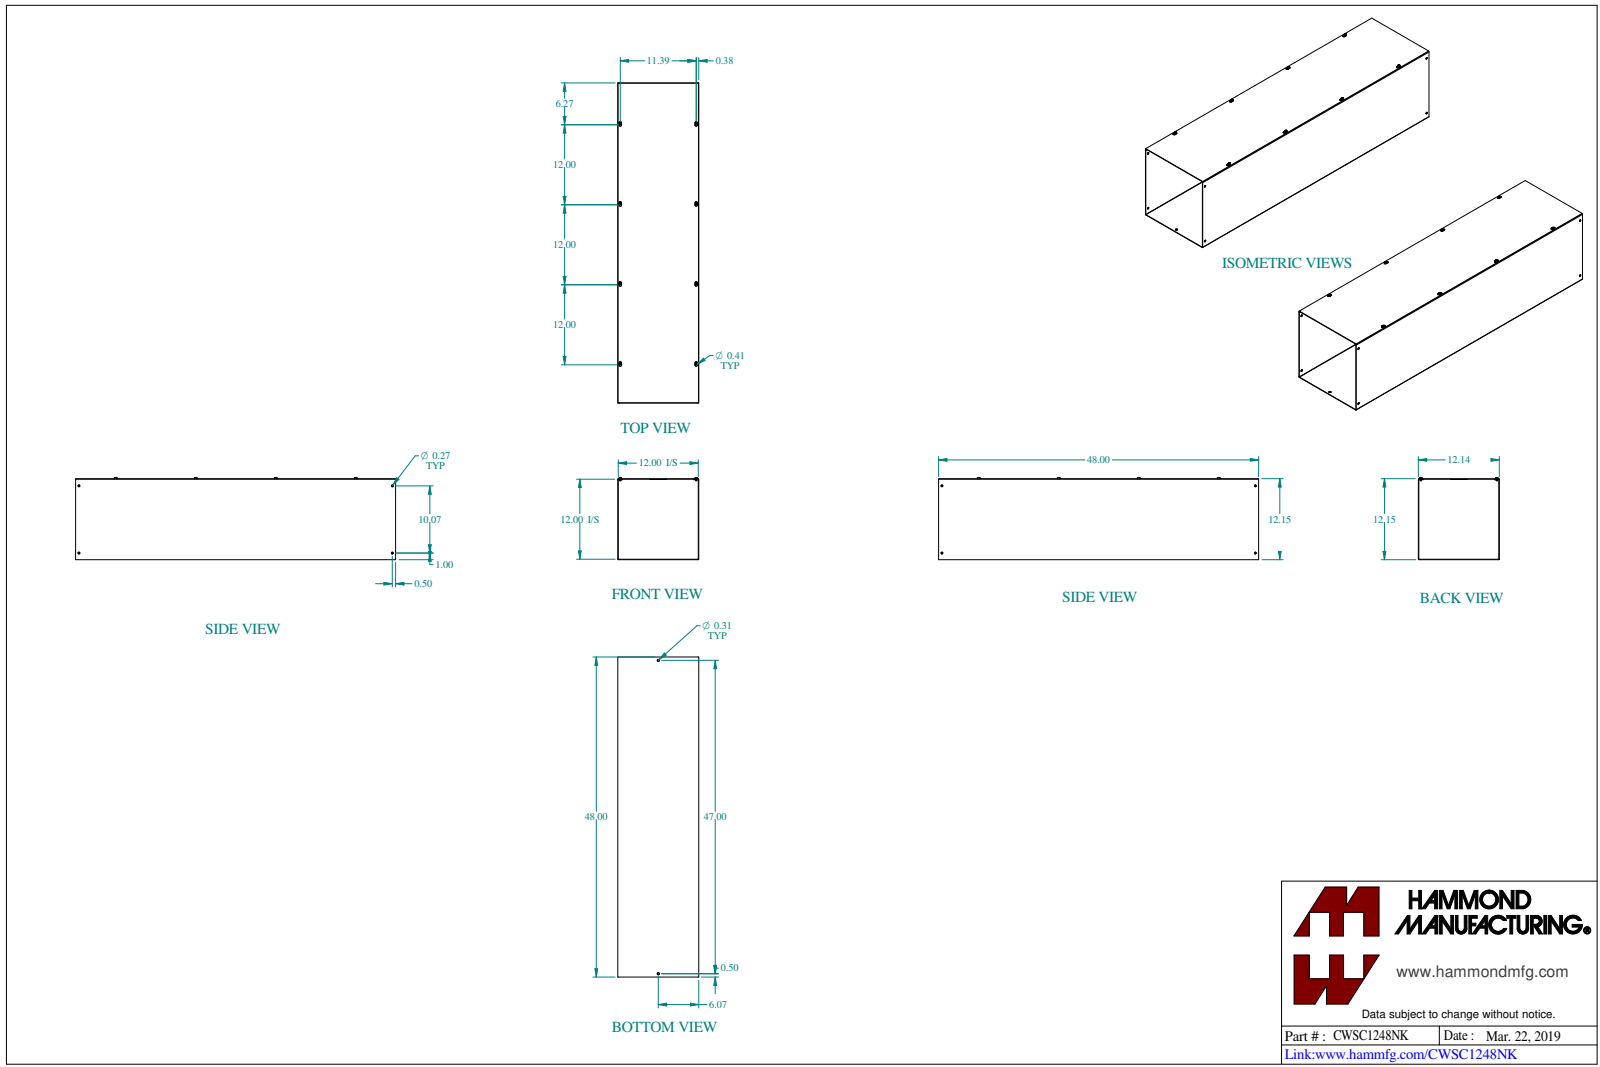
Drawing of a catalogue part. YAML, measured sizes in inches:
part_name: "CWSC1248NK"
step_written_by: "SolidWorks 2023 (CONFIG_CONTROL_DESIGN)"
units: inches
bodies: {solids: 10, faces: 304, planar: 148, cylindrical: 108, other: 48}
overall_size: [48, 12.325, 12.144]
volume: 174.2
surface_area: 4766
round_holes:
  - {diameter: 0.177, count: 8}
  - {diameter: 0.266, count: 4}
  - {diameter: 0.313, count: 2}
round_bosses_or_shafts:
  - {diameter: 0.375, count: 8}
  - {diameter: 0.19, count: 8}
partial_cylinders:
  - {radius: 0.125, count: 8}
  - {radius: 0.203, count: 8}
  - {radius: 0.036, count: 4}
  - {radius: 0.108, count: 4}
face_to_face_distances: [0.072, 12.072, 12, 0.078, 12.15, 12.078, 12.144, 11.928, 0.15, 0.031]
hole_center_spacings: [12, 16.547, 7.919, 11.394, 18.404, 24, 26.567, 30.045]
